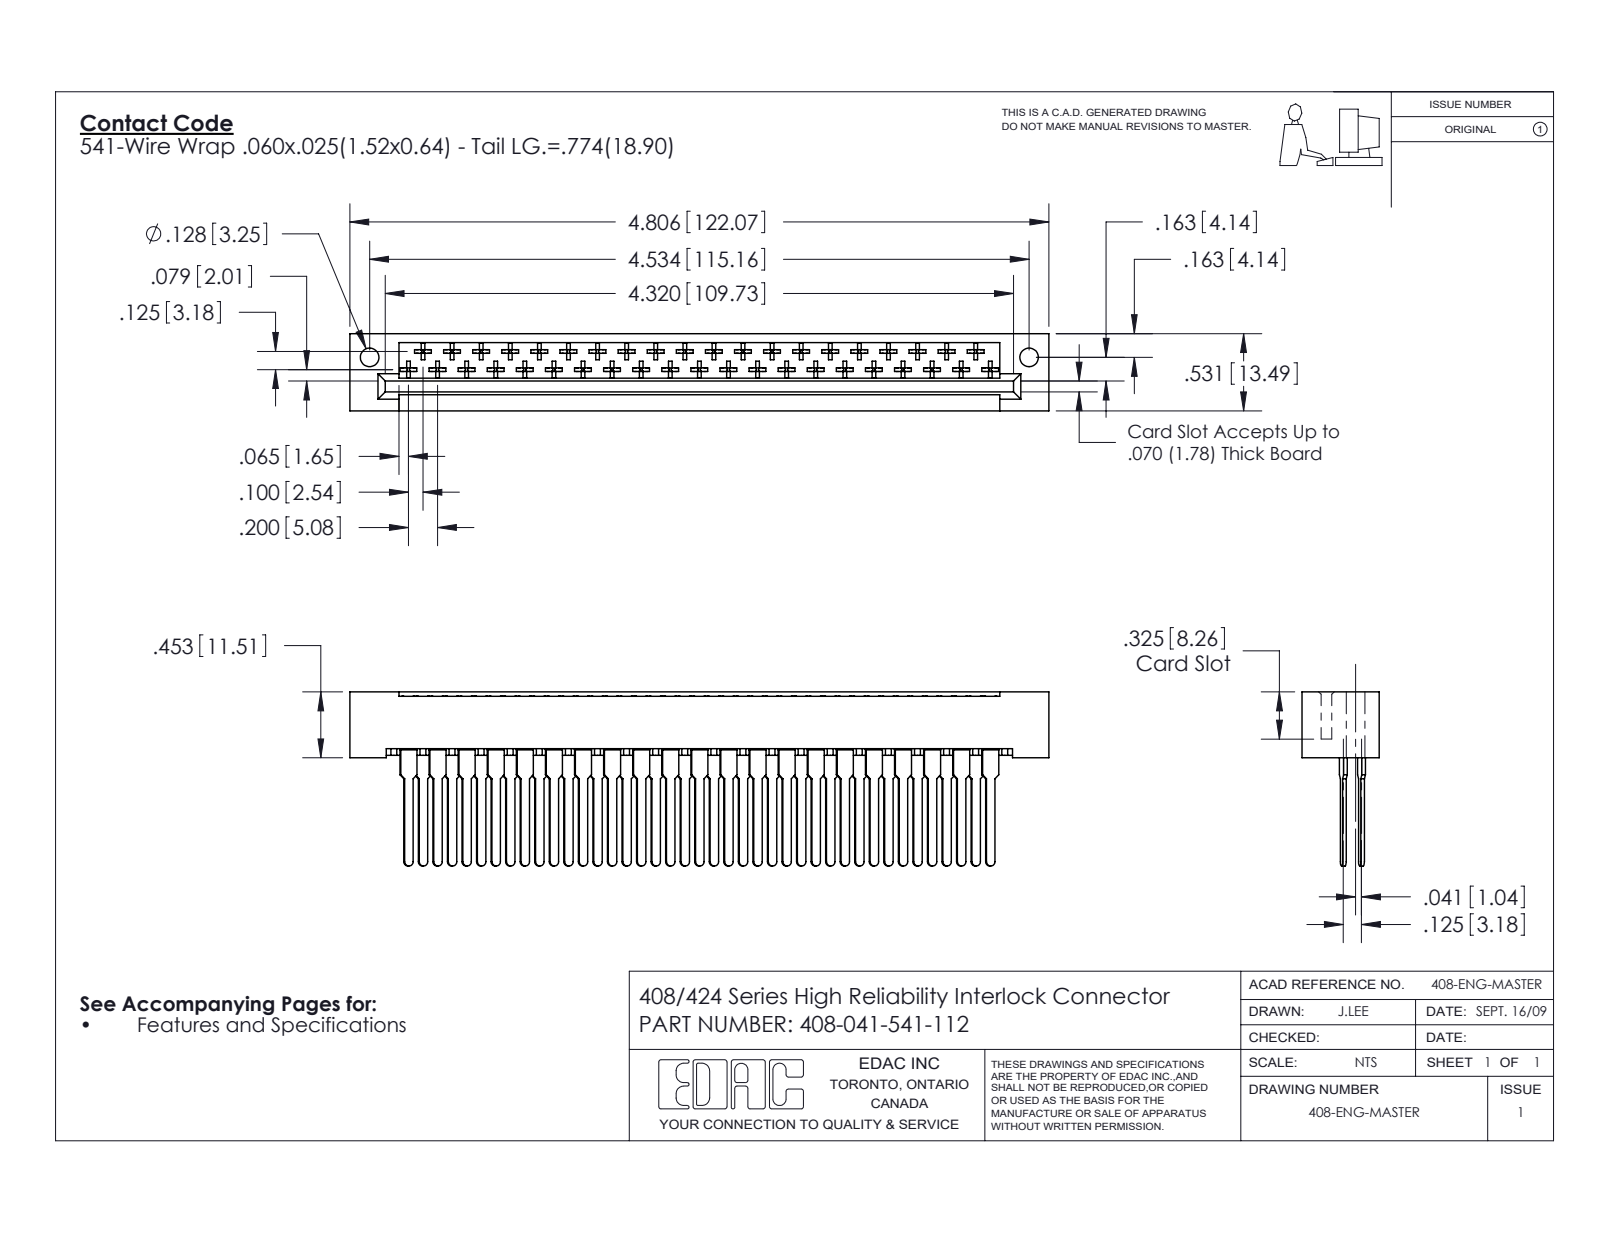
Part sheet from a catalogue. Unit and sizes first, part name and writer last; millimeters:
Units: millimetres
Overall size (bounding box): 122.1 × 30.4 × 13.5
Round holes (diameter × count): ⌀3.3 ×2
Partial cylindrical surfaces — rounded edges, fillets, slot ends (radius × count): R0.3 ×246, R0.5 ×43, R0.8 ×41
Main face-to-face distances: 13.5, 2.5, 3.2, 0.6, 0.6, 10.2, 6.6, 6.9, 6, 7.5
Hole centre spacings: 115.2
Volume: 14 700 mm³ · Surface area: 19 760 mm²
Bodies: 42 solids, 2217 faces (1676 planar, 377 cylindrical, 164 other)
Part name (STEP PRODUCT): 408-041-541-112; 408 Part_041 - 1; 408-290-001_408-290-141
STEP written by: SolidWorks 2016 (CONFIG_CONTROL_DESIGN)
